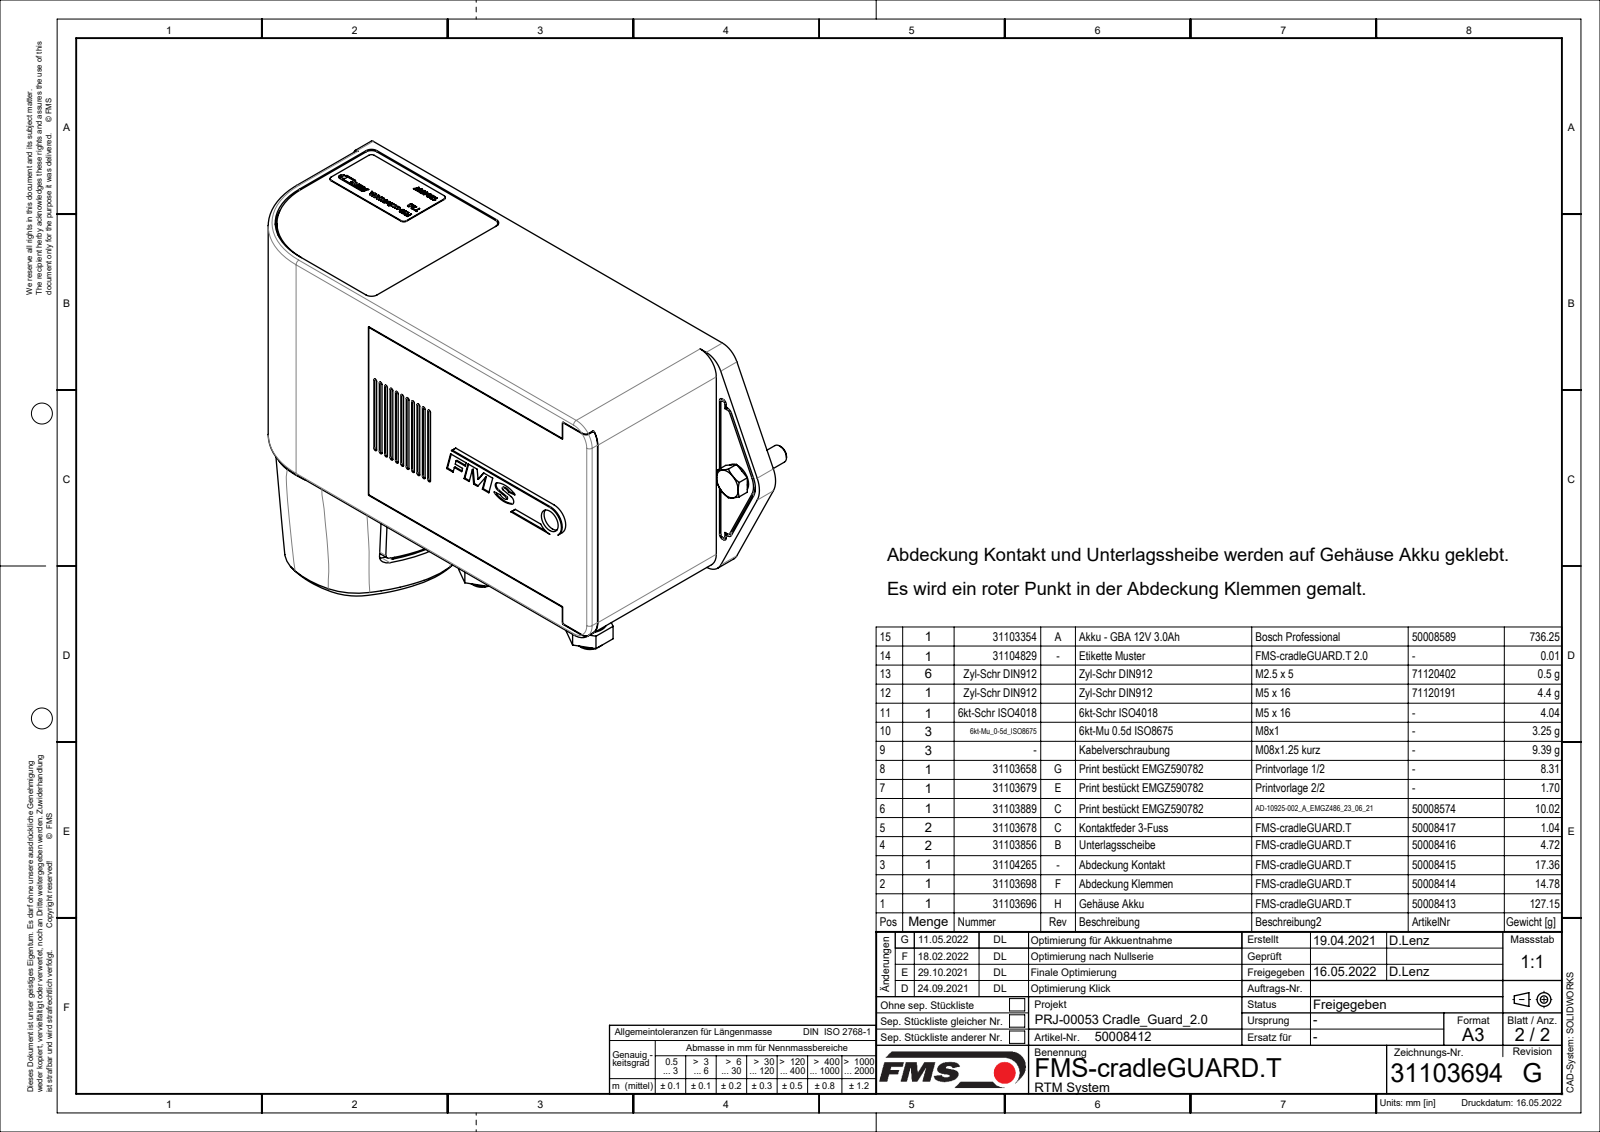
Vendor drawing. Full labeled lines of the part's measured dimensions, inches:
Part name (STEP PRODUCT): 31103696; 31103698_01; 31103658_01; 31103354_01 (+7 more)
STEP written by: SolidWorks 2018 (CONFIG_CONTROL_DESIGN)
Units: inches
Bodies: 15 solids, 1583 faces (641 planar, 572 cylindrical, 370 other)
Overall size (bounding box): 6.535 × 4.23 × 2.835
Volume: 14.92 in³ · Surface area: 213 in²
Round holes (diameter × count): ⌀0.073 ×6, ⌀0.104 ×6, ⌀0.13 ×3, ⌀0.295 ×3, ⌀0.331 ×3, ⌀0.205 ×2, ⌀0.217 ×2, ⌀0.043 ×1, ⌀0.246 ×1
Round bosses / shafts (diameter × count): ⌀0.183 ×6, ⌀0.512 ×3, ⌀0.472 ×3, ⌀0.217 ×3, ⌀0.118 ×3, ⌀0.197 ×2, ⌀0.335 ×1, ⌀0.315 ×1
Partial cylindrical surfaces — rounded edges, fillets, slot ends (radius × count): R0.02 ×99, R0.039 ×92, R0.012 ×81, R0.079 ×24, R0.236 ×11, R0.028 ×9, R0.05 ×8, R0.157 ×7
Main face-to-face distances: 0.079, 2.008, 1.969, 2.638, 0.063, 2.087, 1.89, 0.118, 0.365, 0.286
Hole centre spacings: 0.939, 2.213, 0.157, 0.442, 0.674, 0.844, 0.867, 0.901
